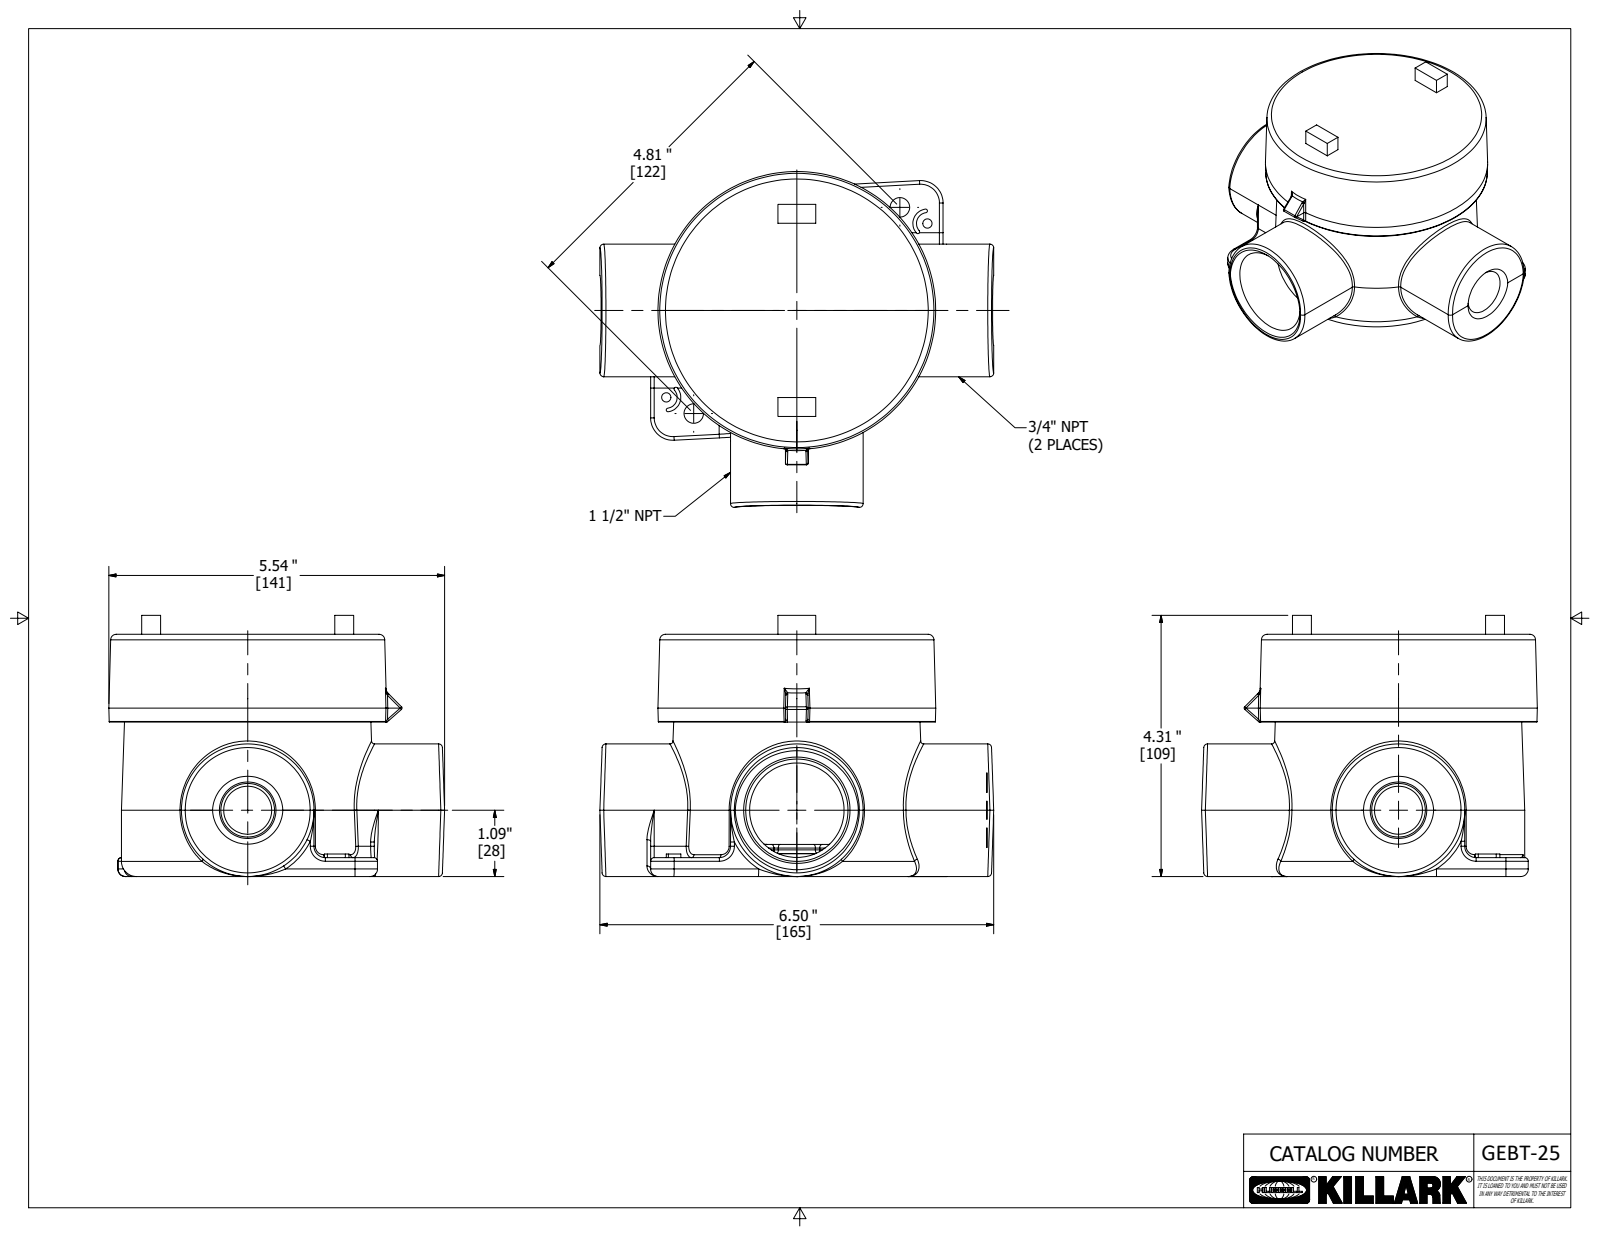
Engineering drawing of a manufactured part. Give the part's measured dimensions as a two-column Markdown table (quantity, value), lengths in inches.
| quantity | value |
| --- | --- |
| part name | GEBT-25; 21656; 21147-override |
| STEP written by | Autodesk Inventor 2020 (AUTOMOTIVE_DESIGN) |
| units | inches |
| bodies | 2 solids, 853 faces (443 planar, 94 cylindrical, 316 other) |
| overall size | 6.5 × 5.542 × 4.31 |
| volume | 38.74 in³ |
| surface area | 213.7 in² |
| round holes (diameter × count) | 0.153 × 2, 0.321 × 2, 1.558 × 2, 0.792 × 1, 3.823 × 1, 4.045 × 1 |
| round bosses / shafts (diameter × count) | 2.188 × 2 |
| partial cylindrical surfaces (radius × count) | 0.06 × 34, 0.03 × 14, 0.125 × 4, 0.031 × 3, 0.187 × 3, 0.18 × 2, 0.24 × 2, 0.37 × 2 |
| main face-to-face distances | 3.998, 3.56, 0.438, 2.549, 1.011, 1.449, 3.5, 0.38, 2.169, 3.18 |
| hole center spacings | 0.527, 4.97, 2.406, 2.406, 2.589, 2.589, 4.812, 5.178 |
